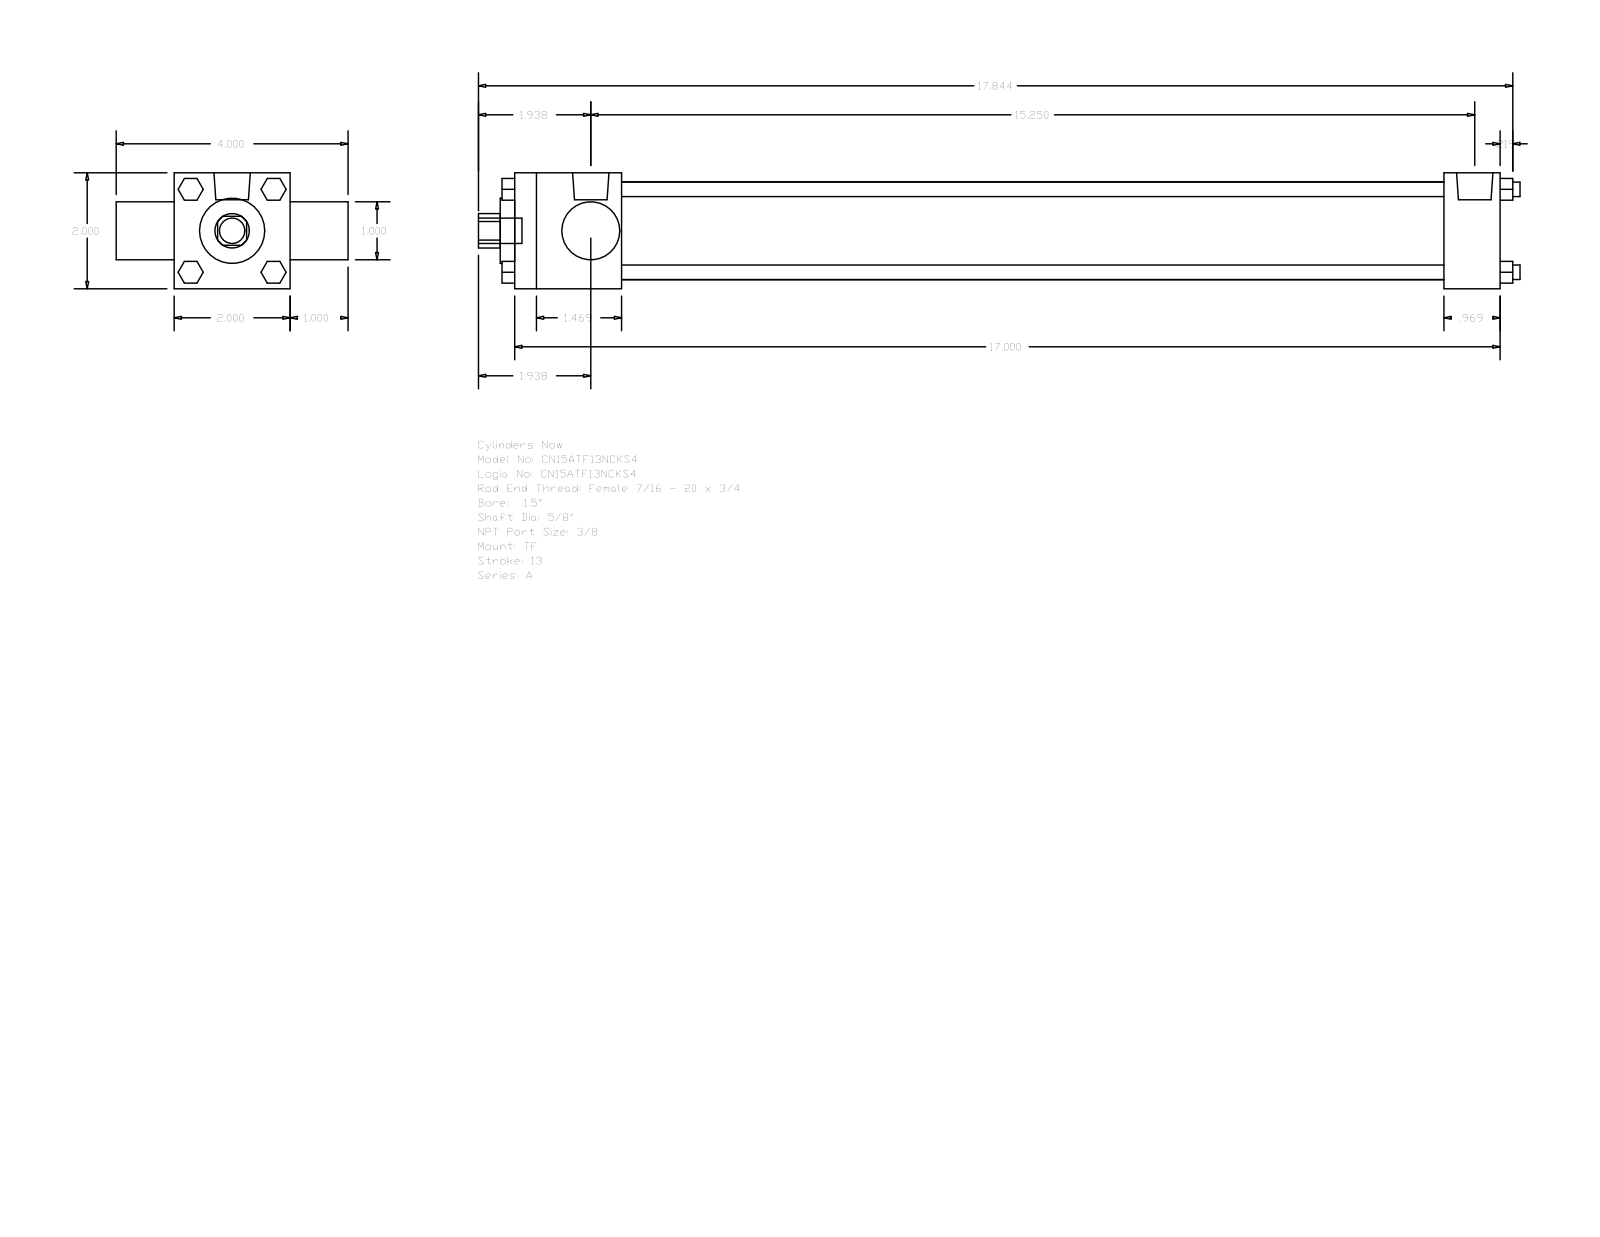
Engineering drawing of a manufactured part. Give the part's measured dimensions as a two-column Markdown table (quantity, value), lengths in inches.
| quantity | value |
| --- | --- |
| part name | A_TF__0150_0.625 |
| STEP written by | GSSL Pune (CONFIG_CONTROL_DESIGN) |
| units | inches |
| bodies | 0 solids, 120 faces (92 planar, 28 cylindrical, 0 other) |
| overall size | 17.969 × 4 × 2 |
| round holes (diameter × count) | 0.625 × 1, 1 × 1, 1.125 × 1, 1.69 × 1 |
| round bosses / shafts (diameter × count) | 0.25 × 4, 0.219 × 3, 0.627 × 2, 0.437 × 1 |
| partial cylindrical surfaces (radius × count) | 0.297 × 1 |
| main face-to-face distances | 2, 17, 1, 3, 1.844, 16.031, 14.187, 15.156, 0.969, 0.375 |
